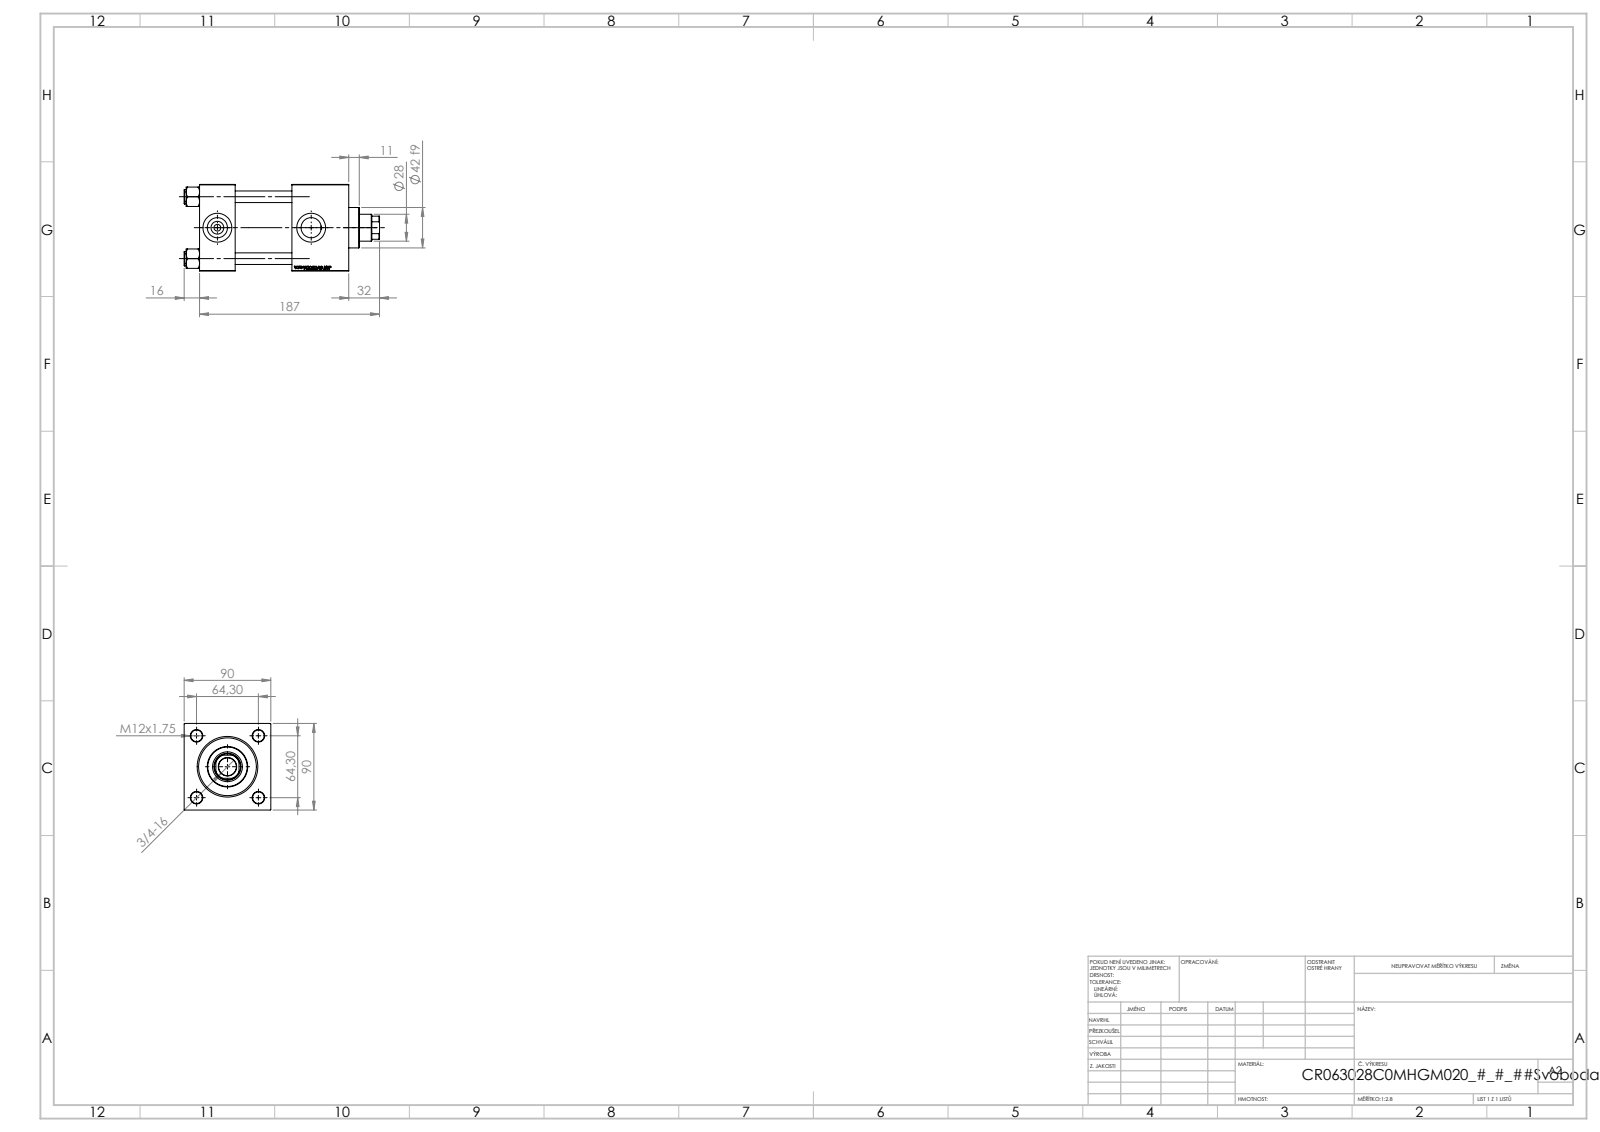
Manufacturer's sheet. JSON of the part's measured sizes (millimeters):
{"part_name": "V215CR_VCP_C; V215CR_C_Body; V215_VC_A; V215CR_C_TYCINKA (+1 more)", "step_written_by": "SolidWorks 2019 (CONFIG_CONTROL_DESIGN)", "units": "millimeters", "bodies": {"solids": 11, "faces": 1148, "planar": 526, "cylindrical": 86, "other": 536}, "overall_size": [203, 90, 90], "volume_mm3": 946885, "surface_area_mm2": 179128, "round_holes": [[12, 4], [7, 2], [20.96, 2], [30, 2], [18.5, 1], [28, 1], [31, 1], [50, 1], [60, 1], [63, 1]], "round_bosses_or_shafts": [[15, 4], [69, 1], [42, 1]], "partial_cylinders_radius": [[13.5, 1]], "face_to_face_distances": [90, 59, 37, 155, 118, 96, 126.3, 89.3, 30.3, 28.7], "hole_center_spacings": [45.47, 64.3, 90.93, 97.5]}
